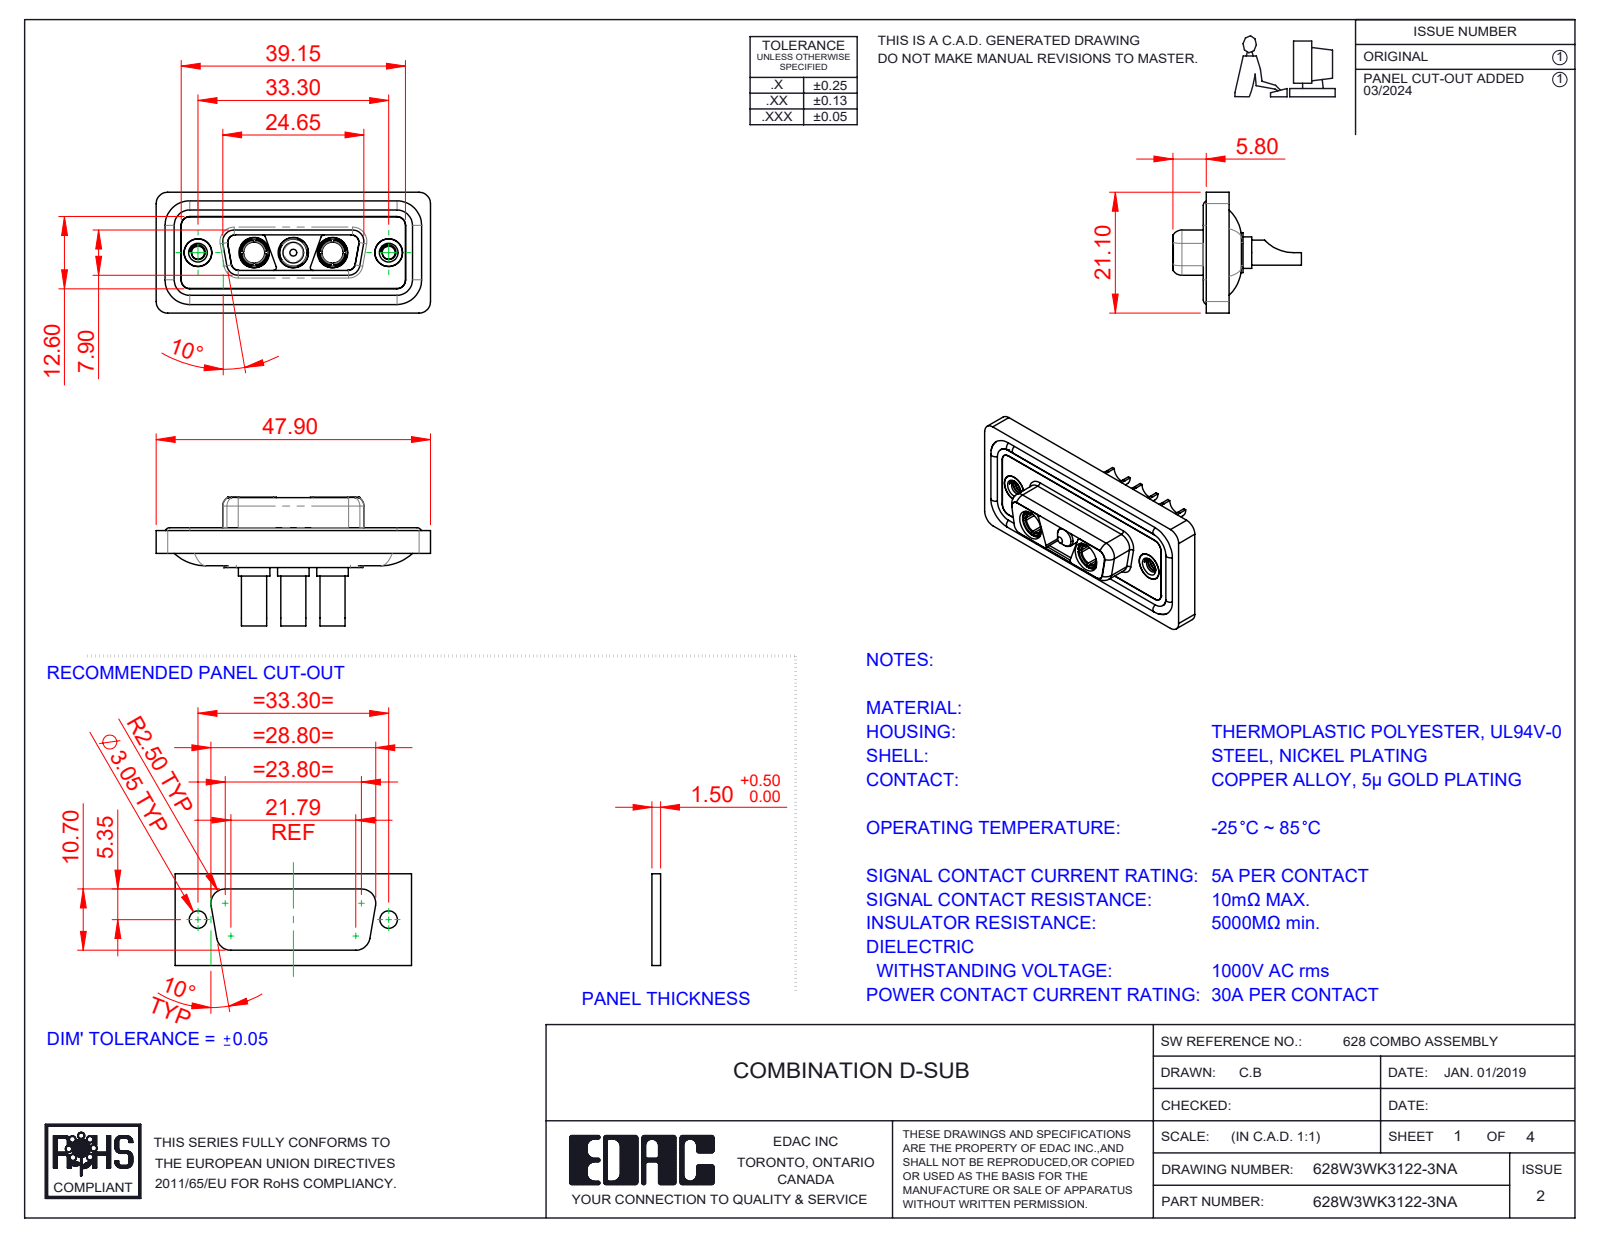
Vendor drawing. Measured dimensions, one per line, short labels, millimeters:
name: Power Socket_30A SC; 628Combo Shell Front_15 Contacts; 628Combo Housing_3WK3; Power Pin_30A SC (+4 more)
written by: SolidWorks 2023 (CONFIG_CONTROL_DESIGN)
unit: mm
bodies: 13 solids, 599 faces (187 planar, 269 cylindrical, 143 other)
size: 47.9 × 22.45 × 21.1
volume: 5 952 mm³; area: 9 825 mm²
holes: 5× ⌀4.85, 3× ⌀3.5, 3× ⌀5.3, 2× ⌀2.26, 2× ⌀3.7, 2× ⌀4, 2× ⌀4.05, 2× ⌀5
bosses: 4× ⌀1.6, 3× ⌀5.5, 3× ⌀5.2, 3× ⌀4.75, 3× ⌀4.4, 3× ⌀3.75, 2× ⌀4.96, 2× ⌀4.95
rounds: 22× R1.5, 20× R2, 12× R1.35, 8× R0.5, 8× R1.6, 4× R0.25, 4× R0.6, 4× R0.65
face distances: 0.4, 1.6, 0.5, 1.1, 2.9, 1.8, 5.65, 7.05, 5.35, 6.6
hole spacings: 6.85, 9.8, 16.65, 23.5, 13.7, 33.3
